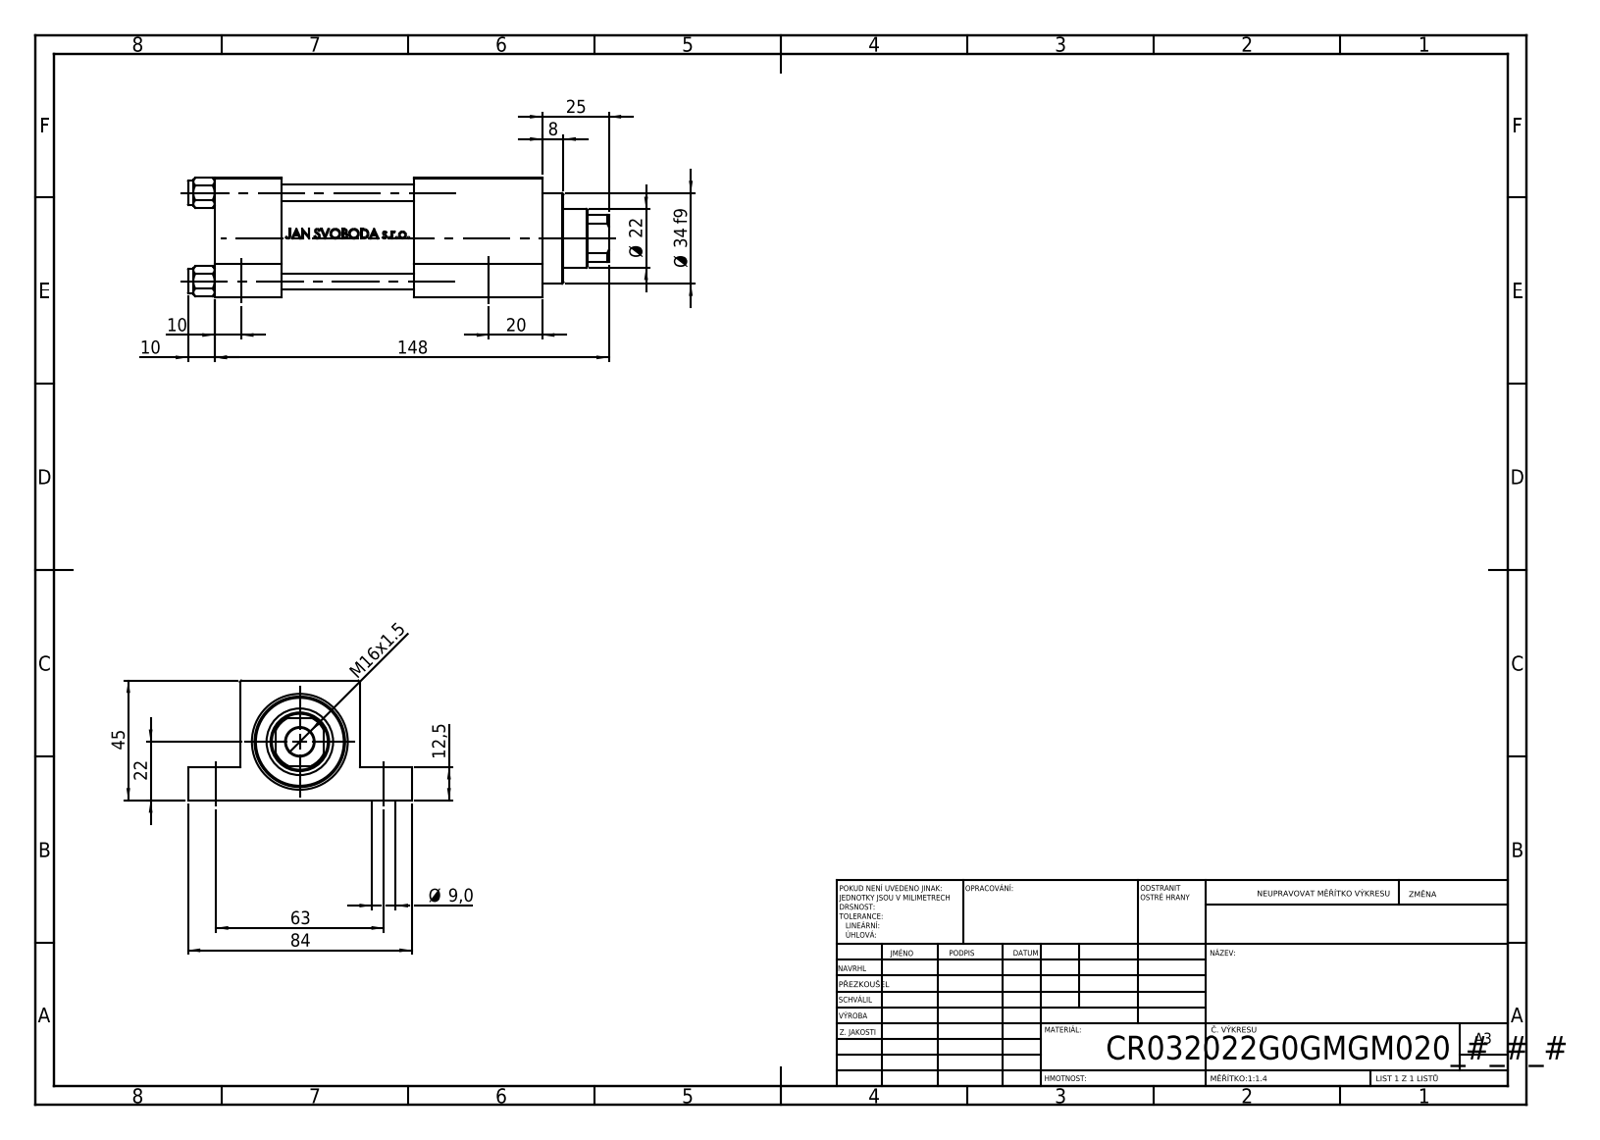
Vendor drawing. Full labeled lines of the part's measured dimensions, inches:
Part name (STEP PRODUCT): V215CR_VCP_G; V215CR_G_Body; V215_VC_A; V215CR_G_TYCINKA (+1 more)
STEP written by: SolidWorks 2019 (CONFIG_CONTROL_DESIGN)
Units: inches
Bodies: 11 solids, 1086 faces (430 planar, 124 cylindrical, 532 other)
Overall size (bounding box): 6.22 × 3.307 × 1.772
Volume: 14.88 in³ · Surface area: 122 in²
Round holes (diameter × count): ⌀0.236 ×4, ⌀0.354 ×4, ⌀0.276 ×2, ⌀0.518 ×2, ⌀0.787 ×2, ⌀0.413 ×1, ⌀0.866 ×1, ⌀0.945 ×1, ⌀0.984 ×1, ⌀1.26 ×1, ⌀1.299 ×1
Round bosses / shafts (diameter × count): ⌀0.354 ×4, ⌀1.496 ×1, ⌀1.339 ×1
Partial cylindrical surfaces — rounded edges, fillets, slot ends (radius × count): R0.413 ×1
Main face-to-face distances: 1.772, 0.984, 0.492, 1.28, 0.768, 2.539, 4.843, 3.858, 1.969, 2.953
Hole centre spacings: 1.307, 0.911, 0.938, 1.848, 2.48, 3.661, 4.422, 2.972
